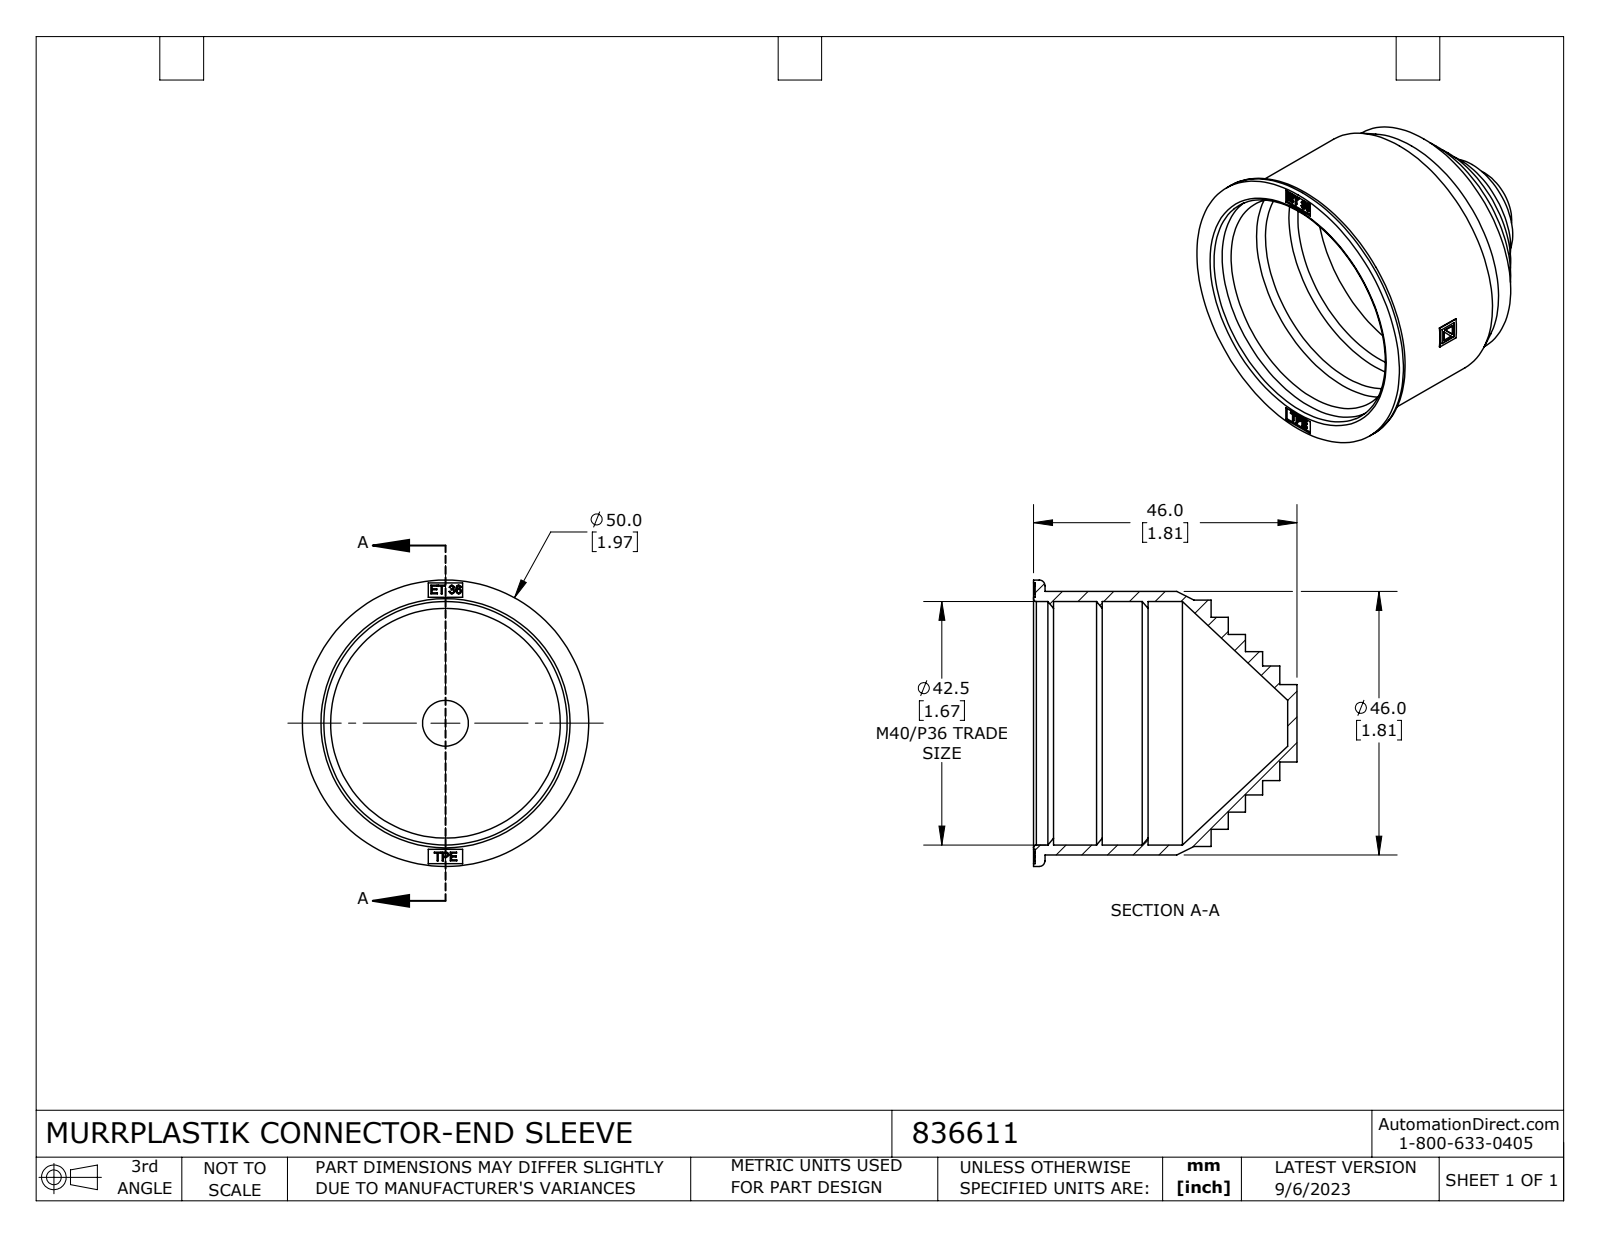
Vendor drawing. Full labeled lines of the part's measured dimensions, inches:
Part name (STEP PRODUCT): 836611
STEP written by: SolidWorks 2021 (CONFIG_CONTROL_DESIGN)
Units: inches
Bodies: 1 solid, 174 faces (97 planar, 28 cylindrical, 49 other)
Overall size (bounding box): 1.969 × 1.969 × 1.811
Volume: 0.743 in³ · Surface area: 21.9 in²
Round holes (diameter × count): ⌀1.673 ×1
Round bosses / shafts (diameter × count): ⌀1.969 ×1, ⌀1.811 ×1, ⌀1.693 ×1, ⌀1.457 ×1, ⌀1.22 ×1, ⌀0.984 ×1, ⌀0.787 ×1, ⌀0.531 ×1
Partial cylindrical surfaces — rounded edges, fillets, slot ends (radius × count): R0.909 ×1
Main face-to-face distances: 0.118, 0.236, 1.22, 0.354, 0.472, 1.339, 0.787, 1.457, 1.575, 1.693
